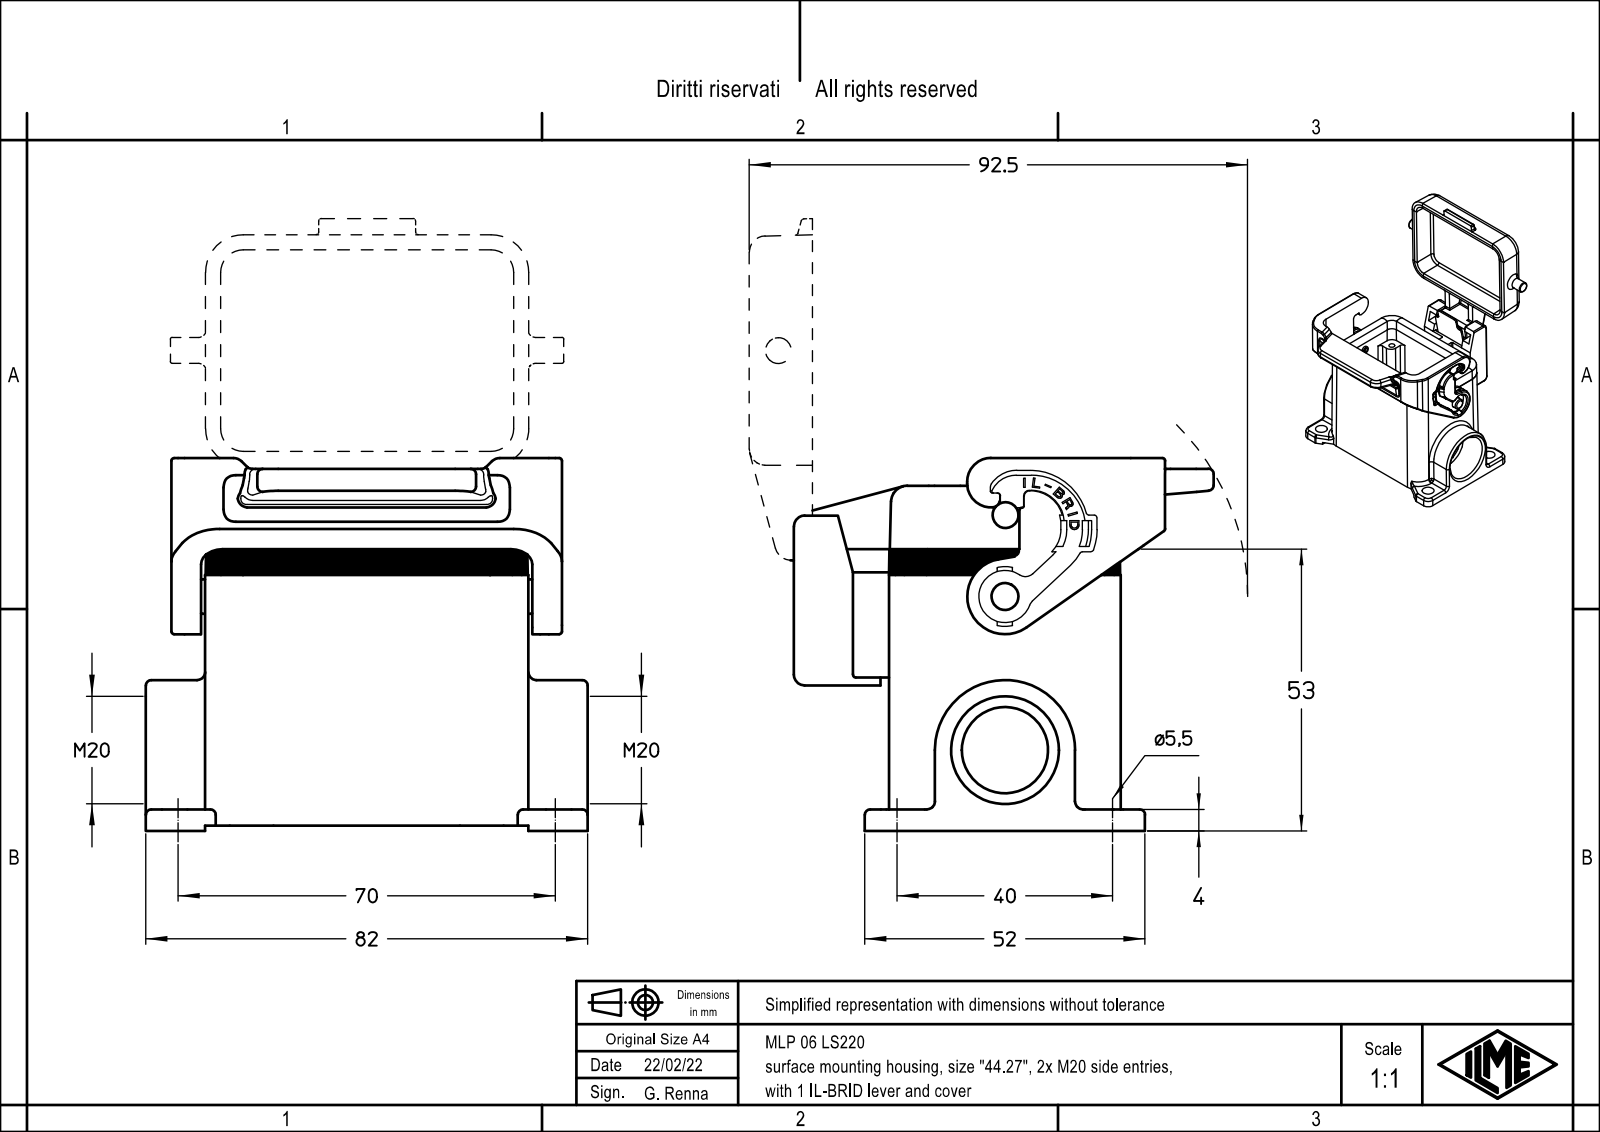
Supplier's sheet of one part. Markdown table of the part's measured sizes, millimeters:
| quantity | value |
| --- | --- |
| part name | MLP_06_LS220 |
| STEP written by | Creo Elements/Direct Modeling 20.1B 02-Apr-2019 (C) Parametric Technology GmbH (AUTOMOTIVE_DESIGN) |
| units | millimeters |
| bodies | 1 solid, 903 faces (568 planar, 259 cylindrical, 76 other) |
| overall size | 113 × 85.85 × 82 |
| volume | 96 550 mm³ |
| surface area | 50 286 mm² |
| round holes (diameter × count) | 2.75 × 4, 5.5 × 4, 16 × 1, 18.6 × 1 |
| round bosses / shafts (diameter × count) | 4.8 × 2, 8 × 1, 6.8 × 1 |
| partial cylindrical surfaces (radius × count) | 1 × 43, 3 × 21, 0.5 × 19, 0.33 × 15, 1.5 × 12, 2 × 11, 7 × 10, 0.3 × 4 |
| main face-to-face distances | 39.25, 3.75, 2, 43, 66.6, 35.5, 23.6, 10, 68.6, 25.6 |
| hole center spacings | 14.53, 35.93, 57.37, 66.12, 27, 40, 44, 51.62 |
